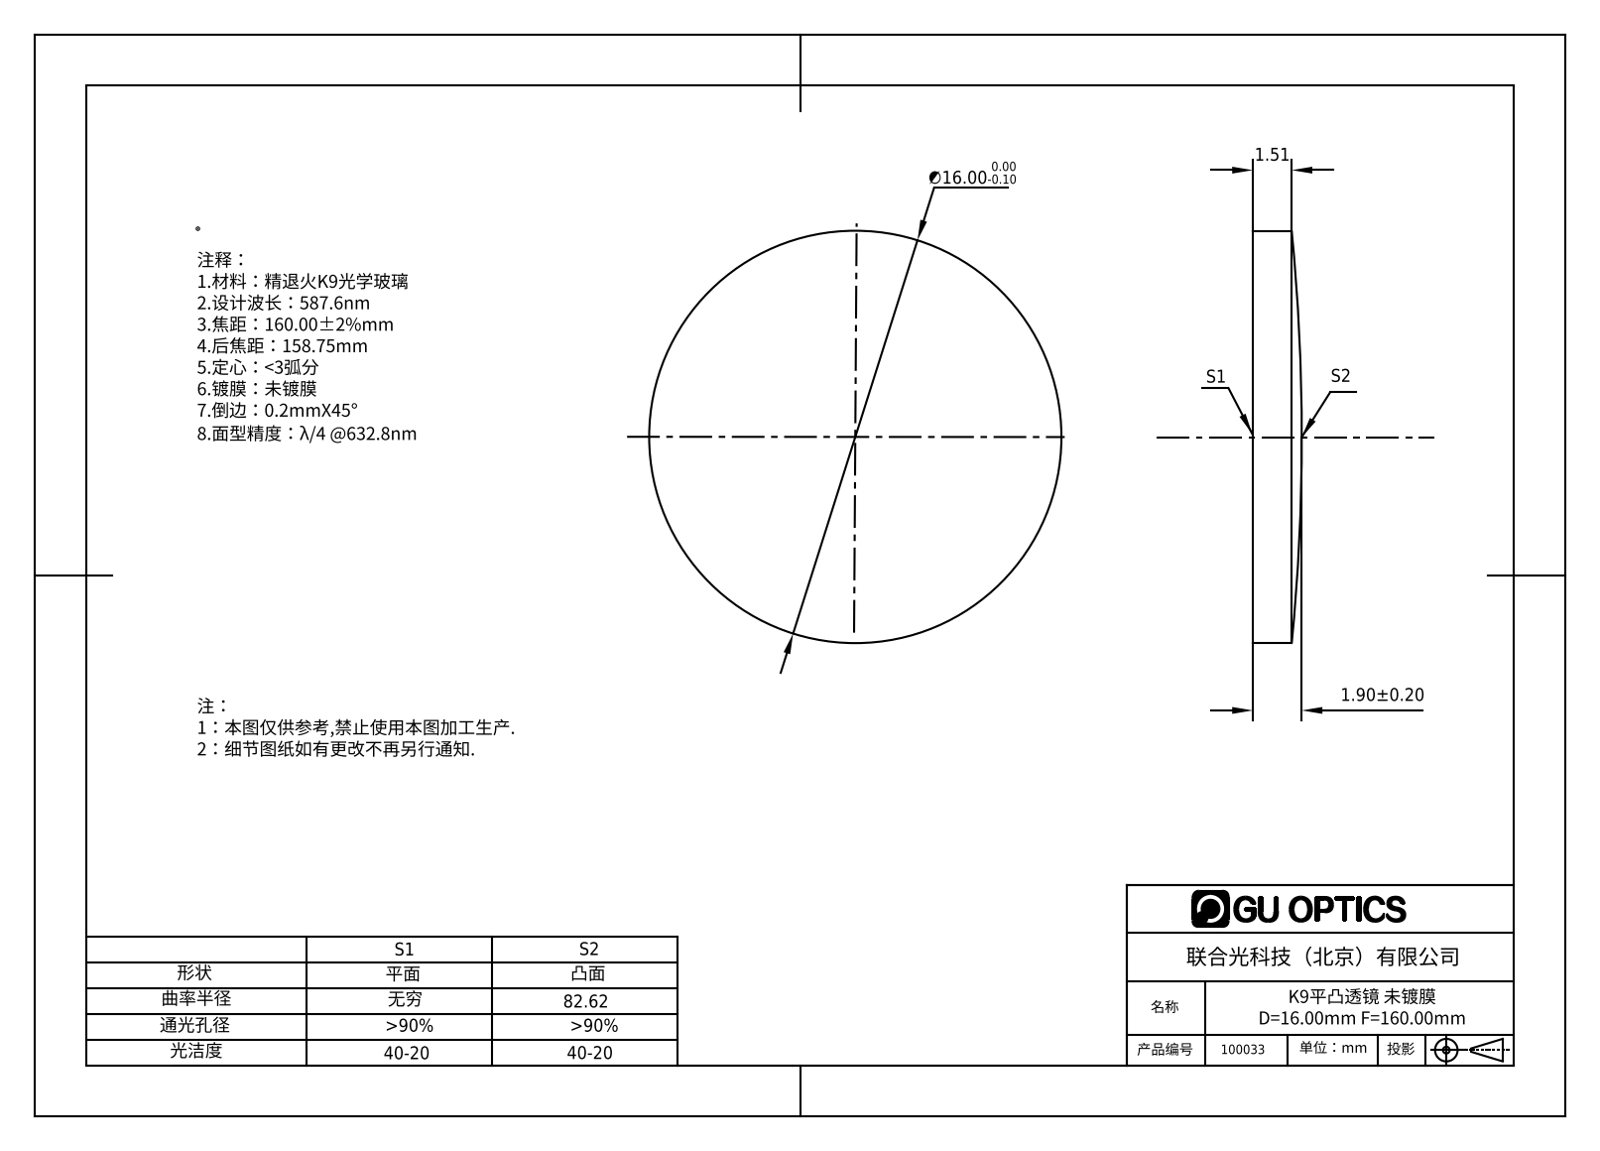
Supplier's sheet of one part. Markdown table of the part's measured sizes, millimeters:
| quantity | value |
| --- | --- |
| part name | 100033 |
| STEP written by | SolidWorks 2016 (AUTOMOTIVE_DESIGN) |
| units | millimeters |
| bodies | 1 solid, 5 faces (1 planar, 2 cylindrical, 2 other) |
| overall size | 16 × 16 × 1.9 |
| volume | 343 mm³ |
| surface area | 478 mm² |
| round bosses / shafts (diameter × count) | 16 × 1 |
